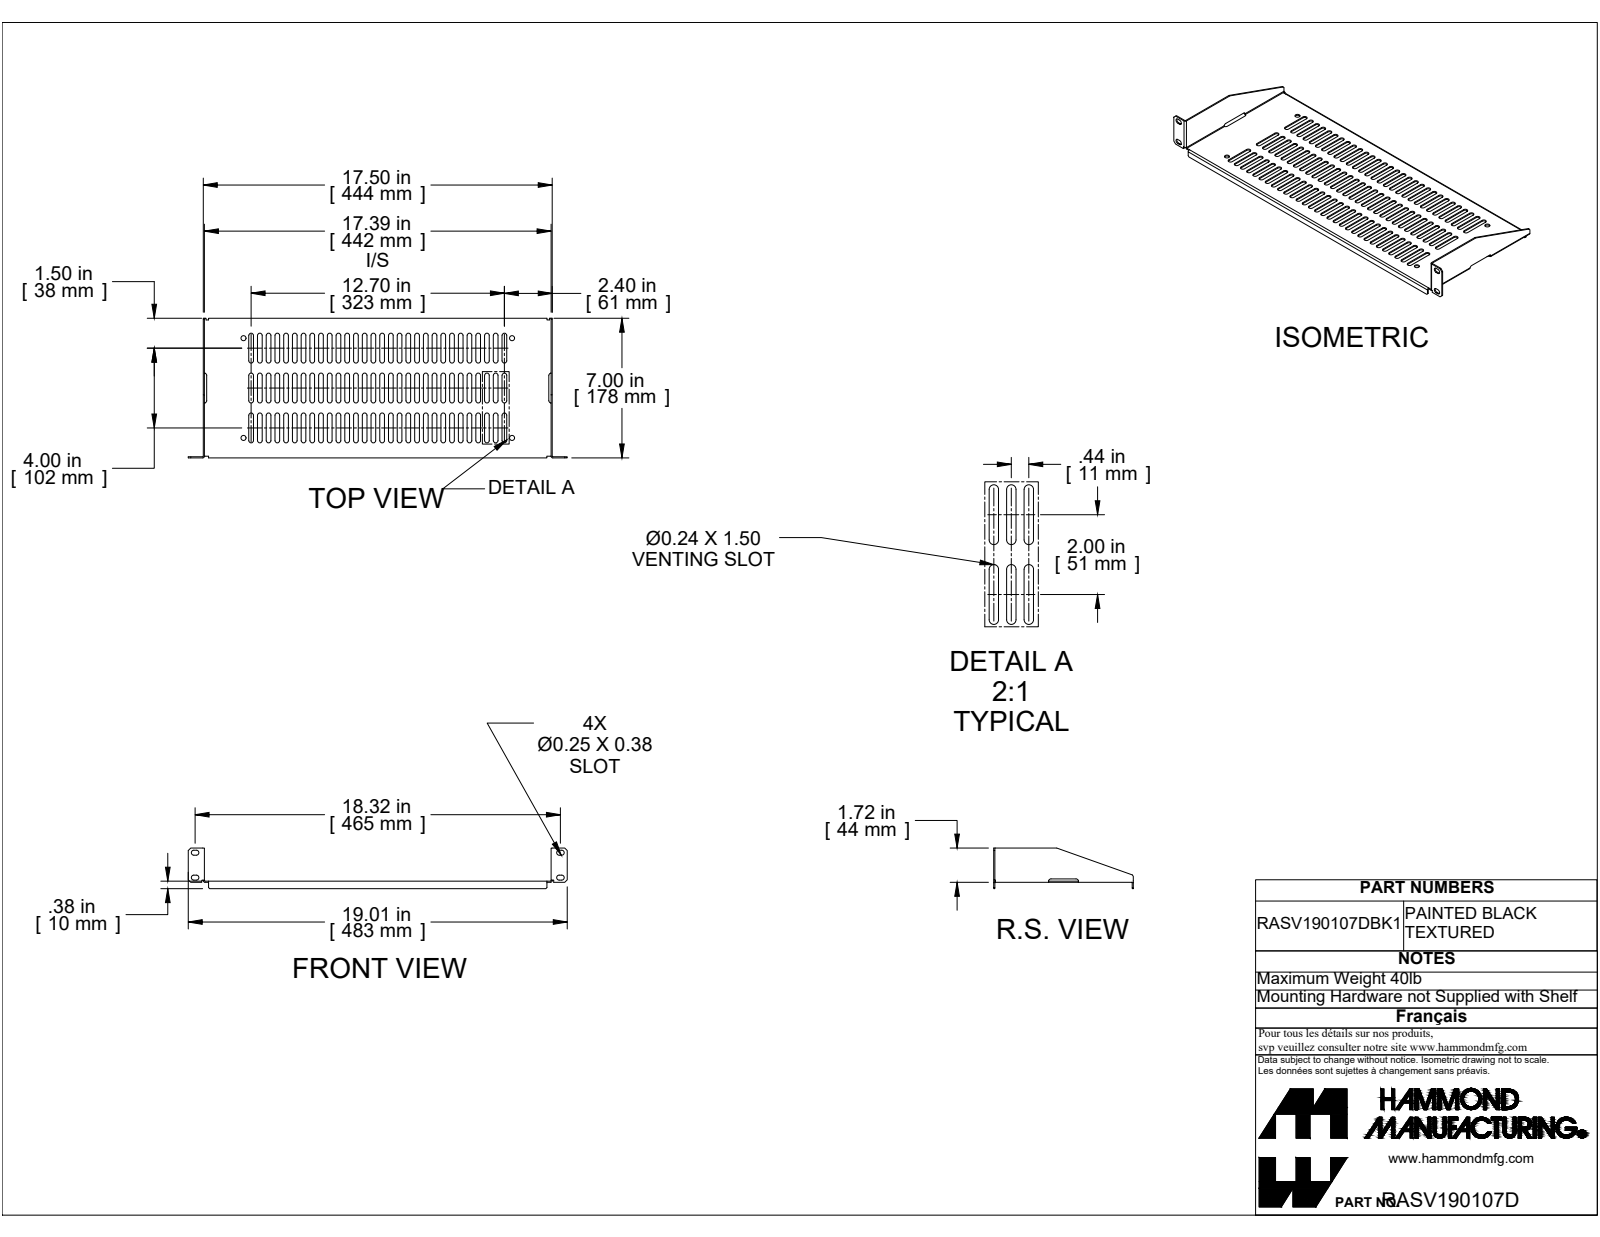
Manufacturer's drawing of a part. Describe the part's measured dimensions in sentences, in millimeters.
The part is named "RASV190107D". Its 3-D file was written by "SolidWorks 2019 (CONFIG_CONTROL_DESIGN)". It is 1 solid with 462 faces: 242 planar, 216 cylindrical and 4 other. Overall it measures 482.8 by 177.8 by 51.7 millimeters. Its volume is 112 600 cubic millimeters and its surface area 169 000 square millimeters. Round holes: 4 of diameter 6.4. Partial cylindrical surfaces (rounded edges, fillets, slot ends): 174 of radius 3, 14 of radius 3.2, 6 of radius 0.7, 6 of radius 2.2, 6 of radius 3. The main face-to-face distances are 1.4, 443.1, 176.4, 444.5, 441.6, 177.8, 174.9, 22.3, 8.1, 9.5. The hole center spacings are 127, 342.1, 364.9.
